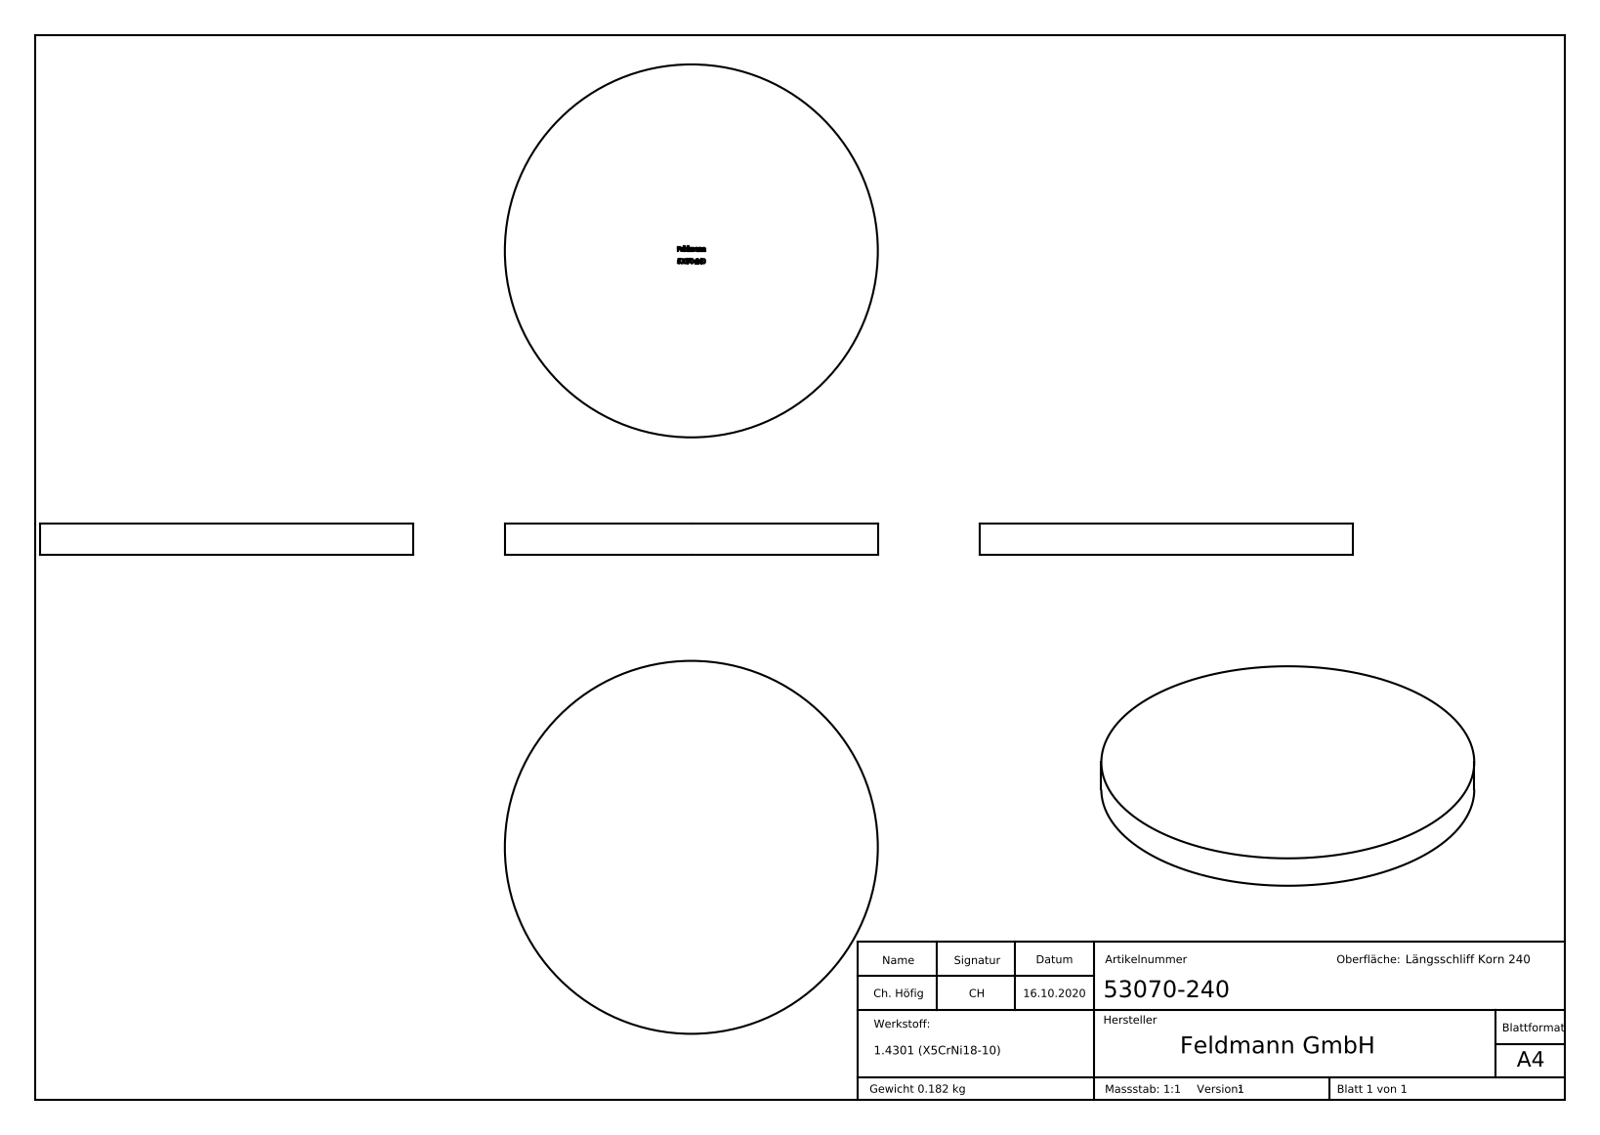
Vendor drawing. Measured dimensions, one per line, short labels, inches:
name: 53070-240
written by: SolidWorks 2018 (CONFIG_CONTROL_DESIGN)
unit: in
bodies: 1 solid, 223 faces (118 planar, 2 cylindrical, 103 other)
size: 2.756 × 2.756 × 0.236
volume: 1.409 in³; area: 13.98 in²
bosses: 1× ⌀2.756
face distances: 0.236, 0.232, 0.07, 0.096, 0.033, 0.095, 0.031, 0.028, 0.039, 0.016
